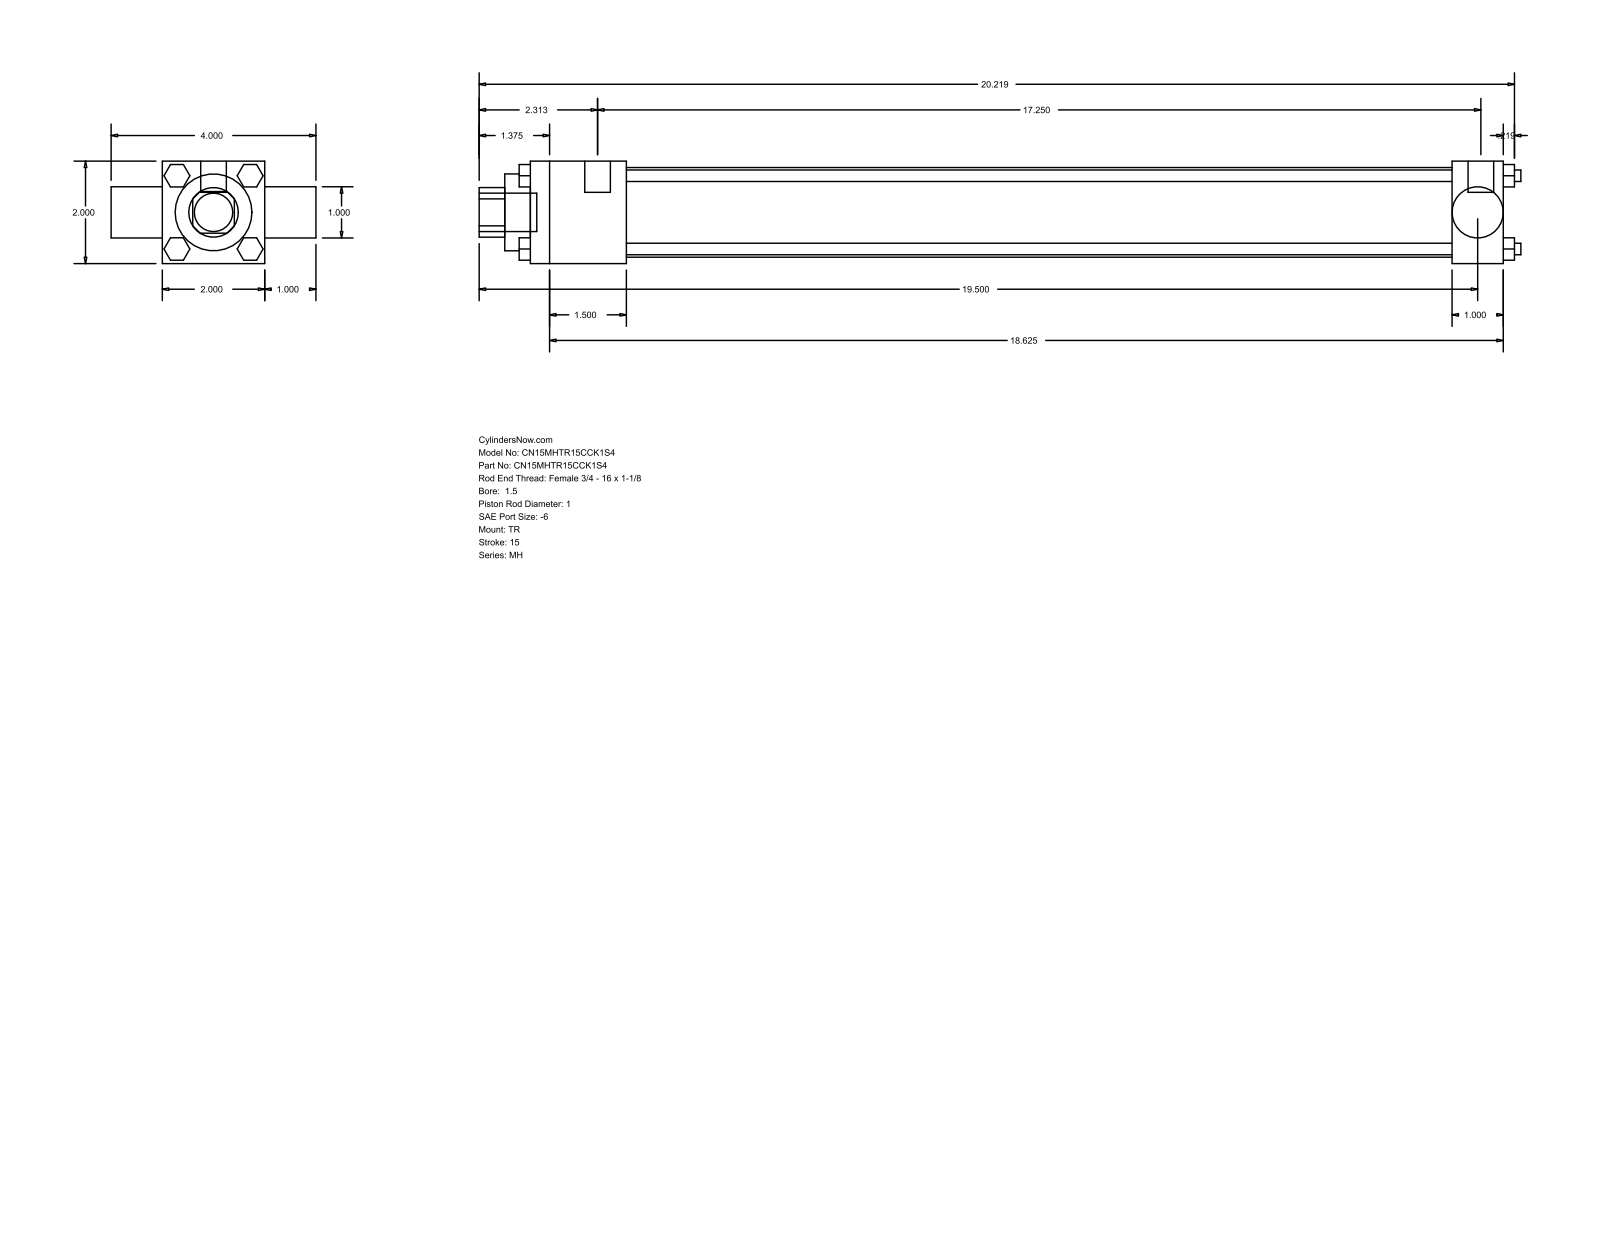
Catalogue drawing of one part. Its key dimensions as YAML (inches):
part_name: "MH_TR__0150_1"
step_written_by: "GSSL Pune (CONFIG_CONTROL_DESIGN)"
units: inches
bodies: {solids: 0, faces: 120, planar: 92, cylindrical: 28, other: 0}
overall_size: [20.344, 4, 2]
round_holes:
  - {diameter: 0.998, count: 1}
  - {diameter: 1, count: 1}
  - {diameter: 1.5, count: 1}
  - {diameter: 1.75, count: 1}
round_bosses_or_shafts:
  - {diameter: 0.225, count: 4}
  - {diameter: 0.219, count: 3}
  - {diameter: 0.5, count: 2}
  - {diameter: 0.75, count: 1}
partial_cylinders:
  - {radius: 0.484, count: 1}
face_to_face_distances: [2, 1, 19, 3, 1.875, 17.125, 18, 16.125, 19.219, 0.5]
